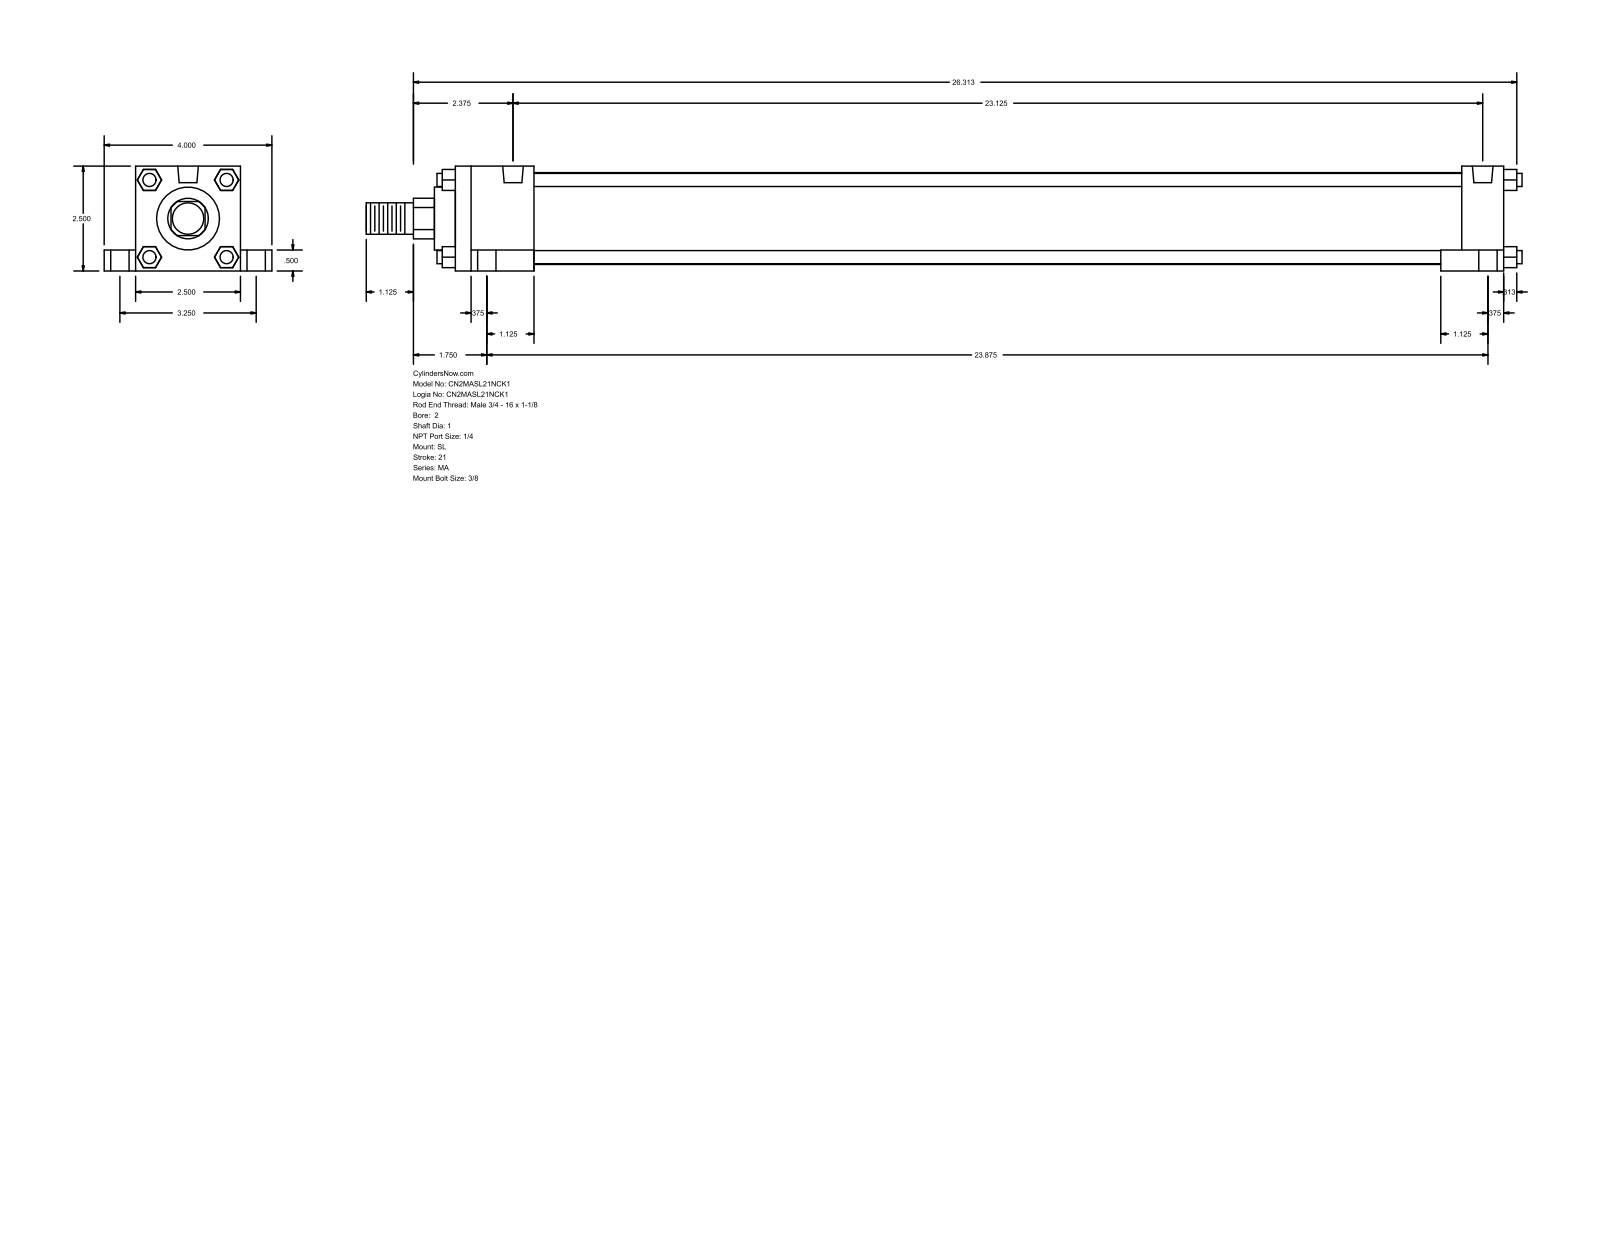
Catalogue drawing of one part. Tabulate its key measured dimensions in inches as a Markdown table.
| quantity | value |
| --- | --- |
| part name | MA_SL__0200_1 |
| STEP written by | GSSL Pune (CONFIG_CONTROL_DESIGN) |
| units | inches |
| bodies | 0 solids, 148 faces (112 planar, 36 cylindrical, 0 other) |
| overall size | 27.563 × 4 × 2.5 |
| round holes (diameter × count) | 0.313 × 4, 0.437 × 4, 0.687 × 4, 0.492 × 2 |
| round bosses / shafts (diameter × count) | 0.313 × 4, 2.19 × 1, 1.5 × 1, 1 × 1, 0.75 × 1 |
| partial cylindrical surfaces (radius × count) | 0.484 × 1 |
| main face-to-face distances | 2.5, 0.5, 25, 0.75, 3.25, 1, 2, 1.875, 23.125, 24 |
| hole center spacings | 1.63, 1.741, 3.25, 23.125, 23.307, 23.806, 23.875, 24.095 |
